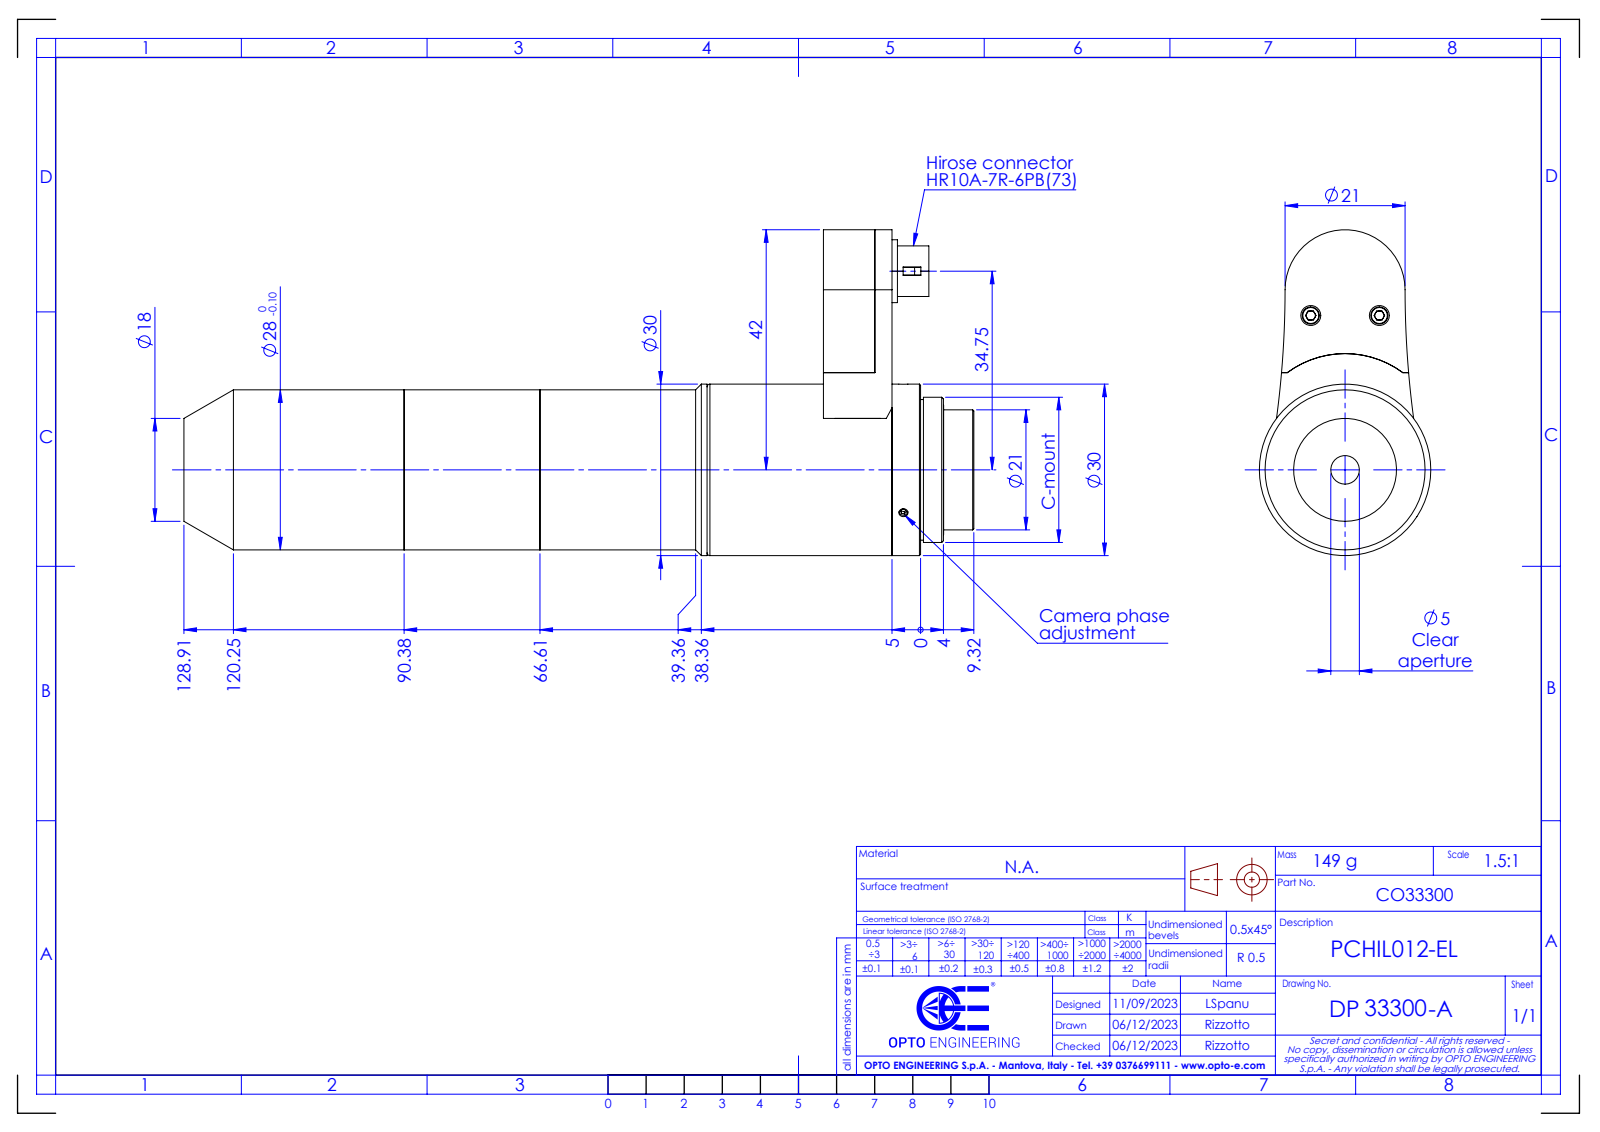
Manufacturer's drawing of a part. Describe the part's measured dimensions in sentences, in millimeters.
The part is named "DP33300-A_PCHIL012-EL". Its 3-D file was written by "SolidWorks 2021 (CONFIG_CONTROL_DESIGN)". It is 0 solids with 188 faces: 73 planar, 78 cylindrical and 37 other. Overall it measures 138.23 by 57 by 30 millimeters. Round holes: 3 of diameter 1.6, 2 of diameter 1.5, 2 of diameter 3.5, 1 of diameter 5, 1 of diameter 7.4, 1 of diameter 10.5. Round bosses or shafts: 2 of diameter 1.2, 1 of diameter 30, 1 of diameter 28, 1 of diameter 25.4, 1 of diameter 24.6, 1 of diameter 23, 1 of diameter 21, 1 of diameter 11. Partial cylindrical surfaces (rounded edges, fillets, slot ends): 2 of radius 169.5, 1 of radius 3.6, 1 of radius 3.9, 1 of radius 4, 1 of radius 10.5. The main face-to-face distances are 12, 111.91, 123.91, 138.23, 26.32, 14.32, 128.91, 17, 5, 9.32. The hole center spacings are 7.9, 9.8, 20.02, 27.66, 35.41, 12, 15.8, 26.85.
